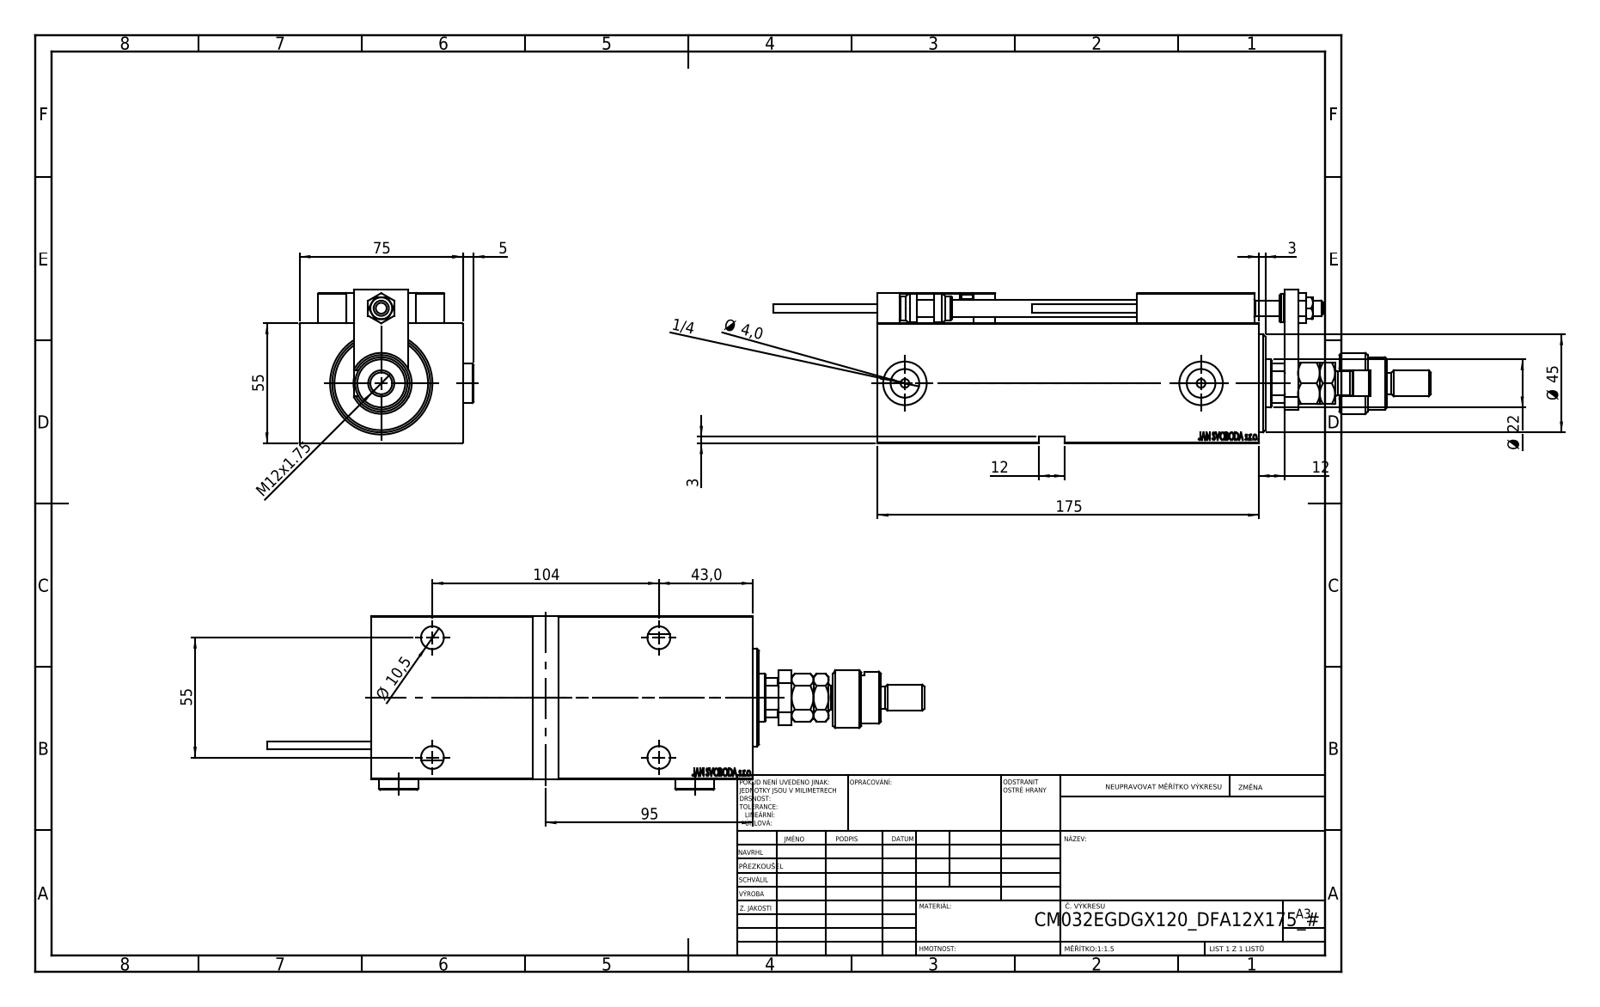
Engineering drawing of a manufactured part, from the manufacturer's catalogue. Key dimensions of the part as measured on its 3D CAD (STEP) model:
Part name (STEP PRODUCT): X_Y_DFA; V450CM_VC_B; ALLEN BOLT D8; FEMALE_PART_FOR_DFA (+8 more)
STEP written by: SolidWorks 2019 (CONFIG_CONTROL_DESIGN)
Units: millimetres
Bodies: 28 solids, 1431 faces (633 planar, 209 cylindrical, 589 other)
Overall size (bounding box): 302 × 79.9 × 70.5
Volume: 715 306 mm³ · Surface area: 138 339 mm²
Round holes (diameter × count): ⌀4 ×6, ⌀8 ×5, ⌀10.5 ×5, ⌀16.5 ×5, ⌀3.2 ×4, ⌀5 ×2, ⌀13.16 ×2, ⌀20 ×2, ⌀7 ×1, ⌀22 ×1, ⌀25.5 ×1, ⌀32 ×1
Round bosses / shafts (diameter × count): ⌀18 ×3, ⌀11 ×2, ⌀5 ×2, ⌀3.8 ×2, ⌀34 ×1, ⌀28 ×1, ⌀24 ×1, ⌀13 ×1
Partial cylindrical surfaces — rounded edges, fillets, slot ends (radius × count): R0.3 ×30, R3 ×2, R9.75 ×1, R10.5 ×1
Main face-to-face distances: 55, 75, 14, 3, 10, 175, 12, 18, 5, 25
Hole centre spacings: 11.37, 20, 28.9, 29.59, 29.69, 36.06, 40.03, 42.19
